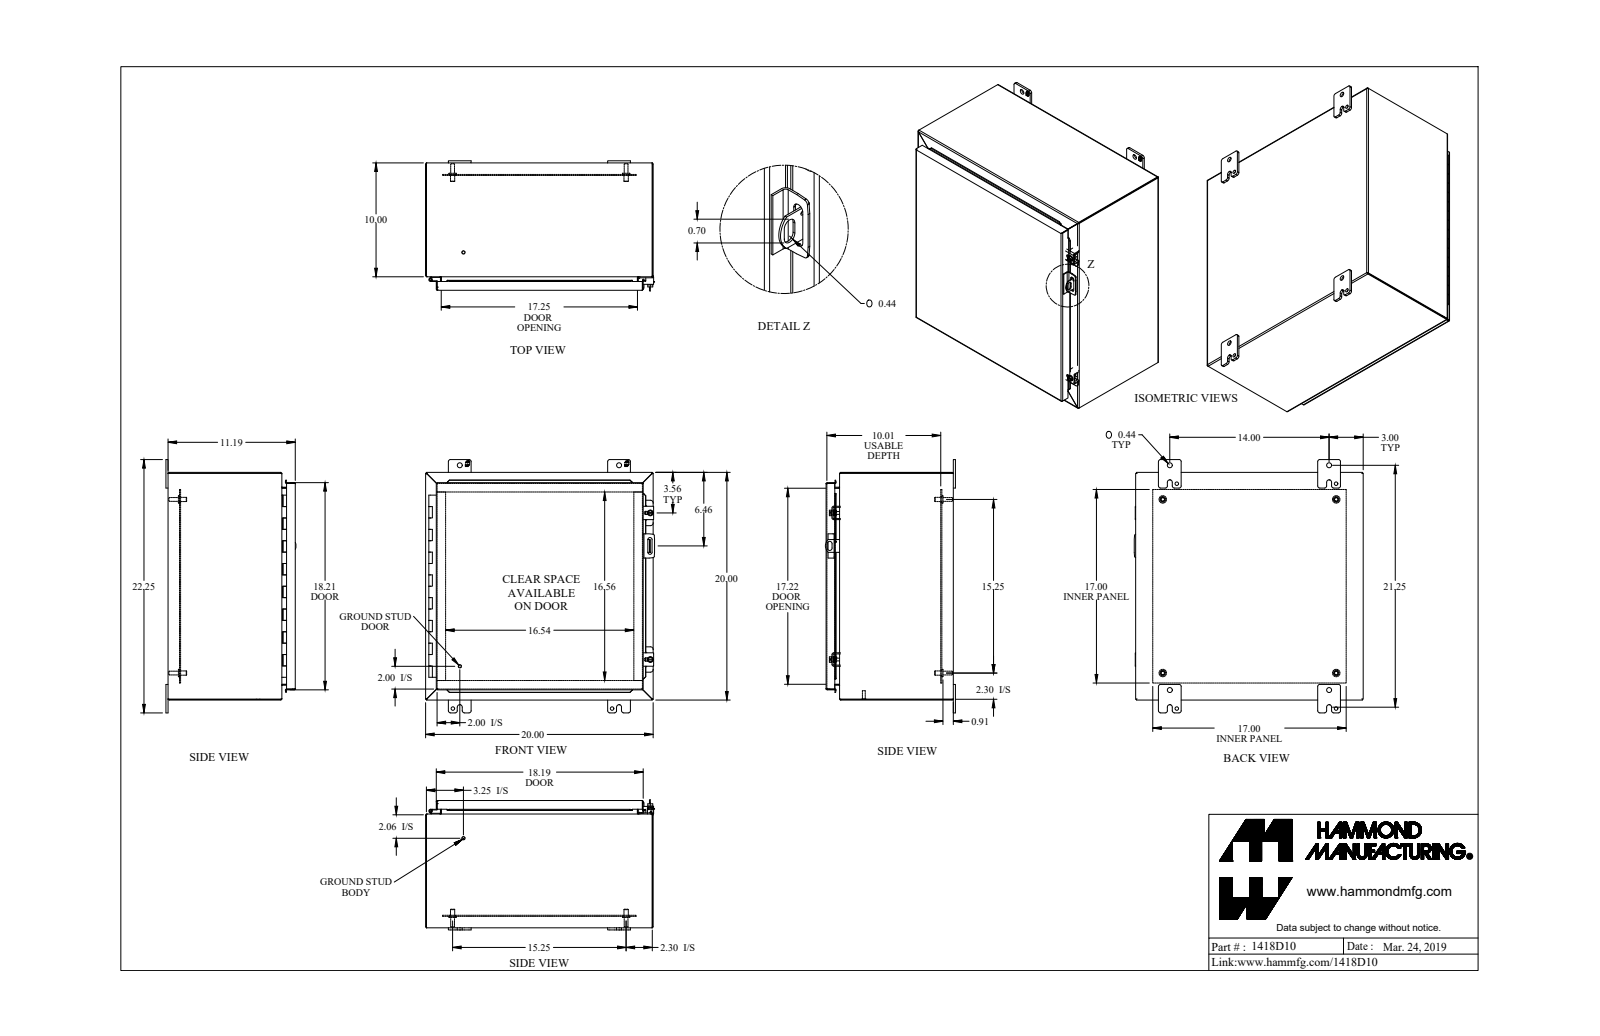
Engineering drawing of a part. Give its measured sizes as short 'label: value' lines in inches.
name: 1418D10
written by: SolidWorks 2019 (AUTOMOTIVE_DESIGN)
unit: in
bodies: 38 solids, 962 faces (667 planar, 247 cylindrical, 48 other)
size: 22.25 × 20.125 × 11.437
volume: 172.5 in³; area: 4 505 in²
holes: 4× ⌀0.313, 4× ⌀0.437, 4× ⌀0.5, 2× ⌀0.213, 2× ⌀0.265, 2× ⌀0.307, 2× ⌀0.375, 2× ⌀0.445, 1× ⌀0.125, 1× ⌀0.187
bosses: 4× ⌀0.65, 4× ⌀0.375, 4× ⌀0.33, 2× ⌀1, 2× ⌀0.5, 2× ⌀0.39, 2× ⌀0.281, 2× ⌀0.25
rounds: 26× R0.188, 20× R0.036, 20× R0.108, 13× R0.048, 13× R0.143, 8× R0.045, 8× R0.218, 8× R0.25
face distances: 0.072, 19.928, 11.113, 11.041, 19.856, 20, 11.185, 0.937, 1.009, 0.095
hole spacings: 15.25, 14, 21.567, 1.736, 3.065, 15.25, 16.762, 19.75
